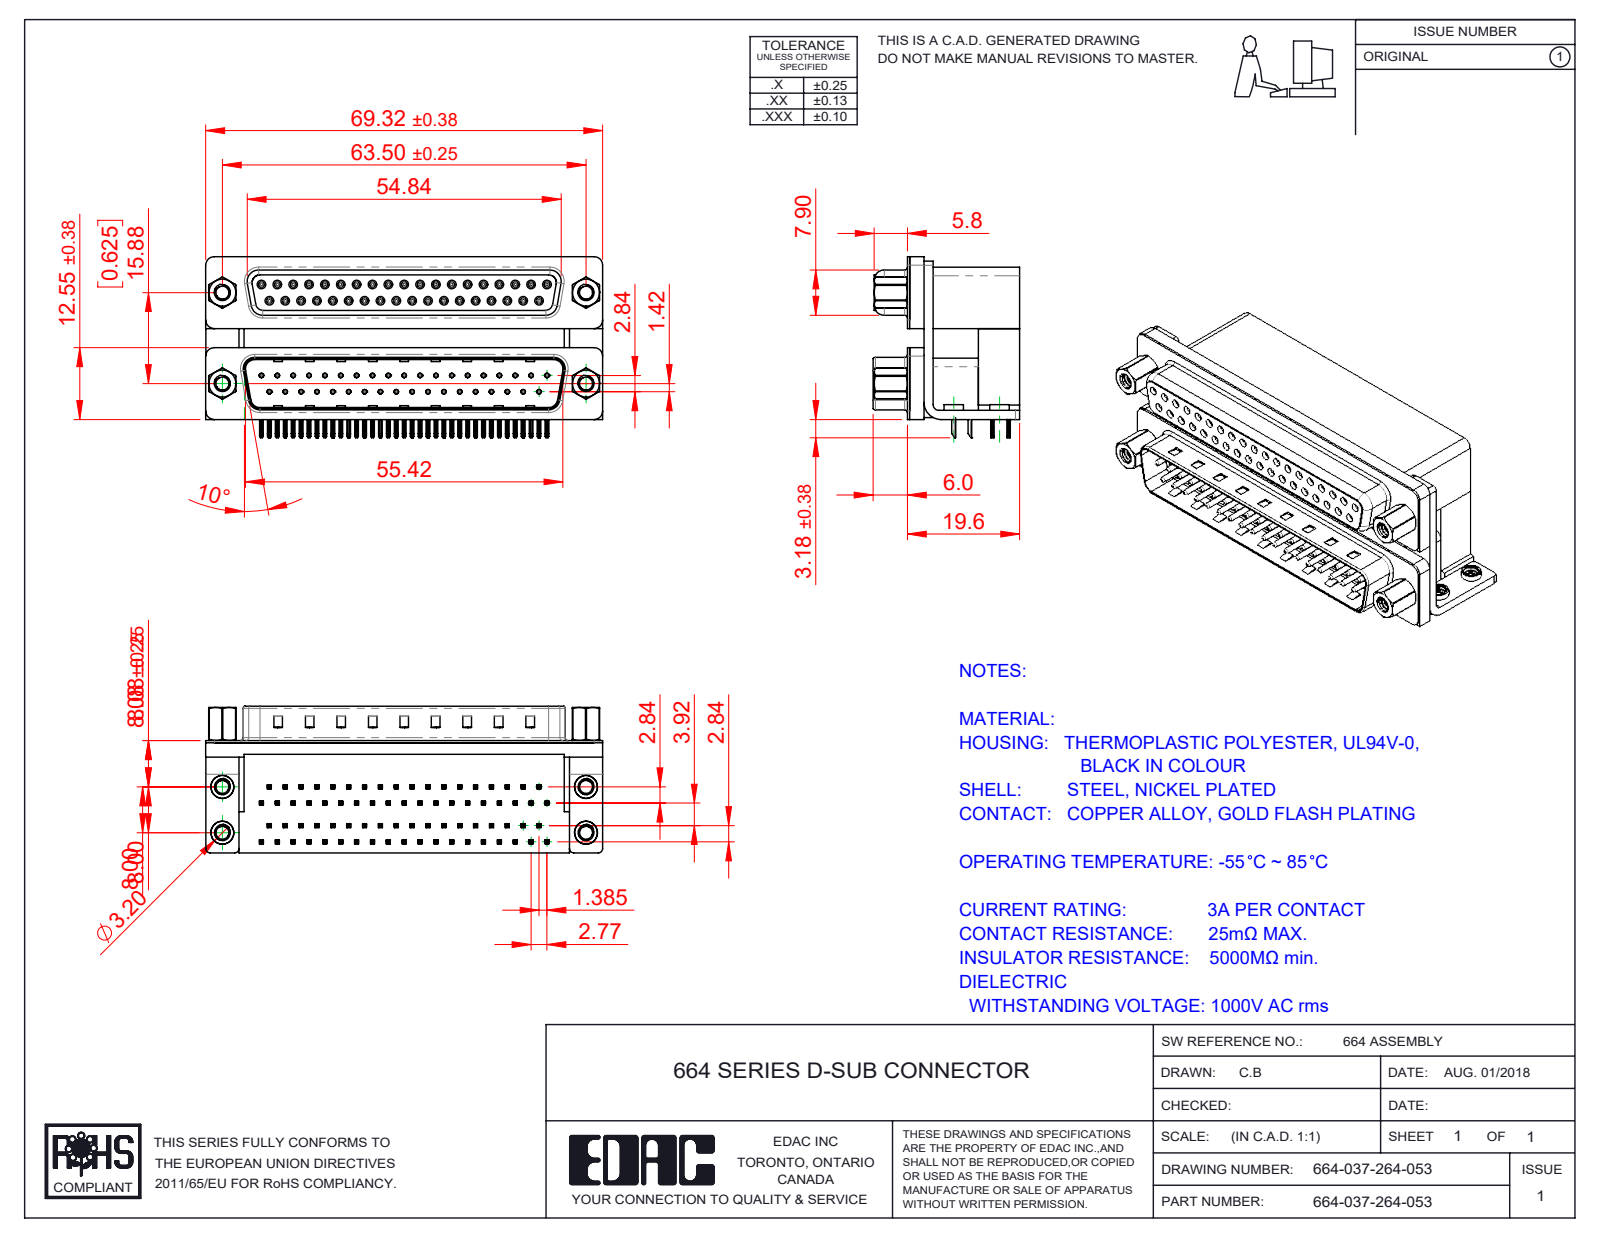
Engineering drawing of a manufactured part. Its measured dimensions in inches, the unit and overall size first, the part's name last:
Units: inches
Overall size (bounding box): 2.729 × 1.244 × 1.008
Round holes (diameter × count): ⌀0.031 ×74, ⌀0.014 ×37, ⌀0.035 ×37, ⌀0.089 ×8, ⌀0.09 ×4, ⌀0.108 ×4, ⌀0.126 ×4, ⌀0.138 ×4, ⌀0.157 ×4, ⌀0.189 ×4, ⌀0.197 ×4
Round bosses / shafts (diameter × count): ⌀0.047 ×37, ⌀0.03 ×37, ⌀0.193 ×4, ⌀0.187 ×4, ⌀0.157 ×4, ⌀0.154 ×4, ⌀0.134 ×4, ⌀0.11 ×4
Partial cylindrical surfaces — rounded edges, fillets, slot ends (radius × count): R0.004 ×296, R0.006 ×148, R0.01 ×148, R0.005 ×74, R0.014 ×74, R0.013 ×37, R0.011 ×18, R0.059 ×13
Main face-to-face distances: 0.016, 0.756, 0.283, 0.472, 0.086, 0.611, 0.112, 1.032, 0.421, 0.525
Hole centre spacings: 0.109, 0.218, 0.124, 0.327, 0.436, 0.545, 0.654, 0.763
Volume: 1.846 in³ · Surface area: 50.63 in²
Bodies: 93 solids, 9337 faces (4797 planar, 2397 cylindrical, 2143 other)
Part name (STEP PRODUCT): 664 Contact Top Lower; 664 Housing Upper_37 Contacts L; 664 Shell Receptacle_37 Contacts; 664 4-40 Threaded Board Mount (+8 more)
STEP written by: SolidWorks 2020 (CONFIG_CONTROL_DESIGN)
